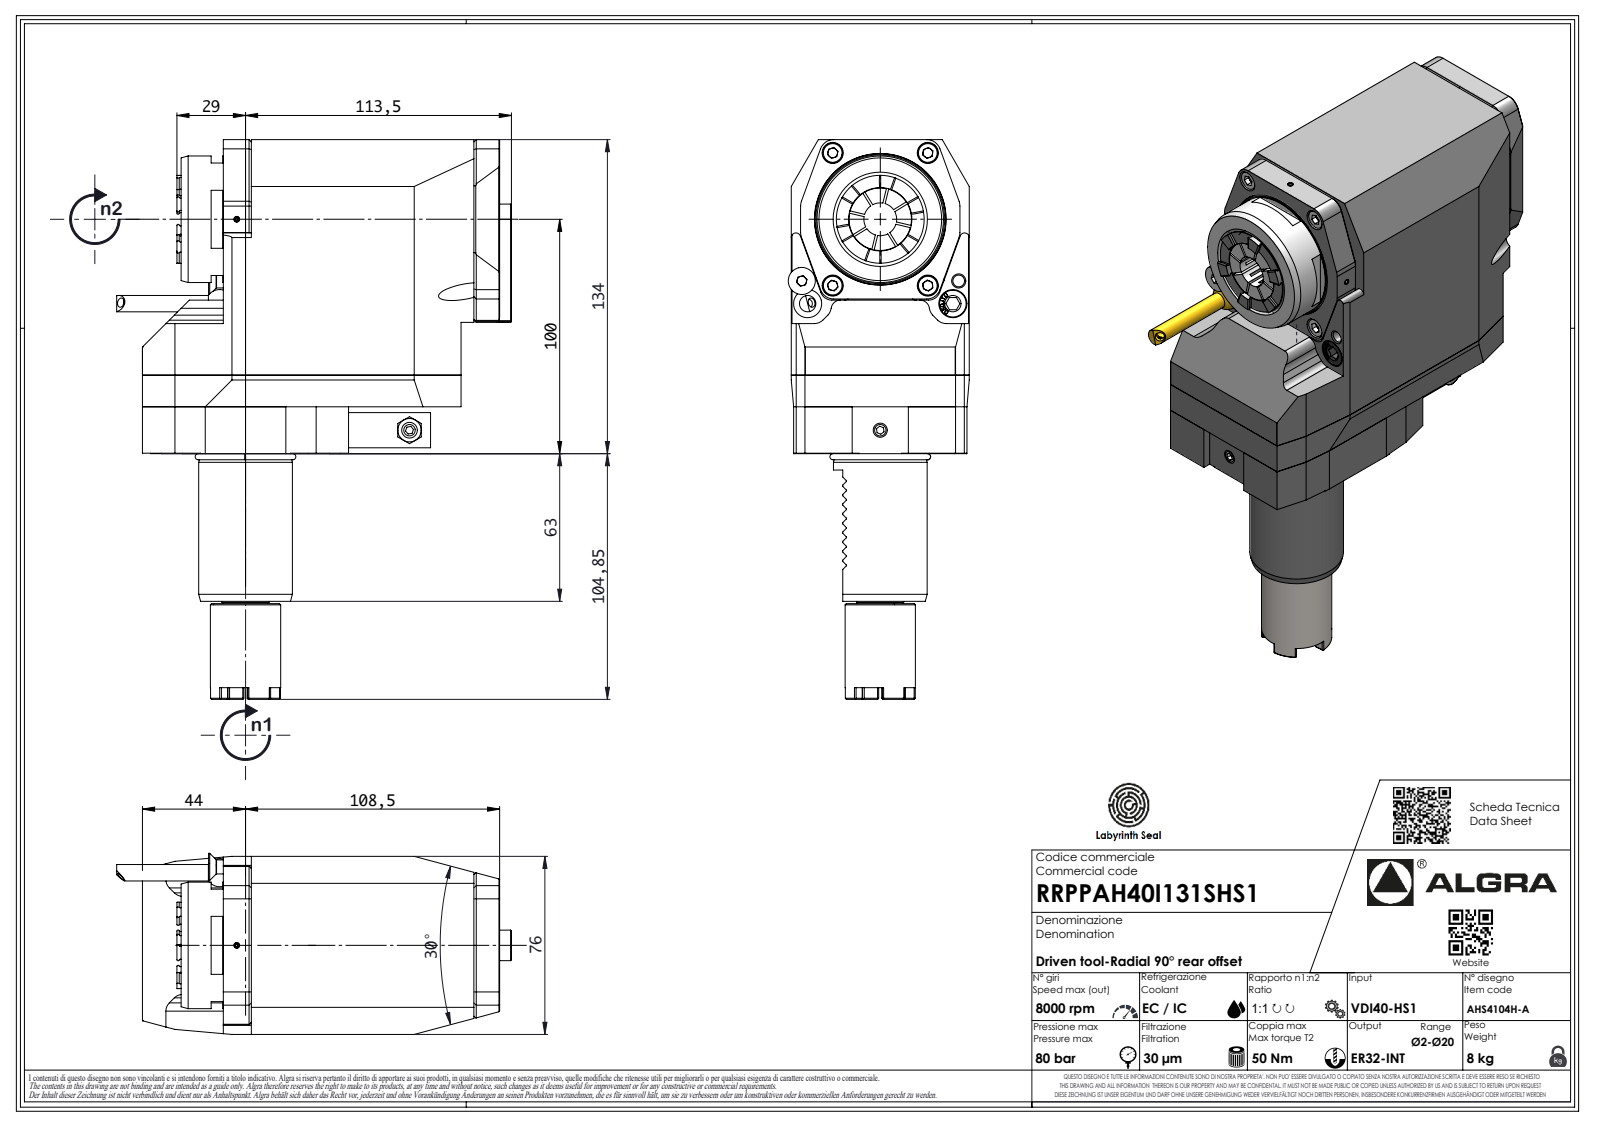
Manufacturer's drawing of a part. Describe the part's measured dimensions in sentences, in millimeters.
The part is named "RRPPAH40I131SHS1". Its 3-D file was written by "SolidWorks 2023 (AUTOMOTIVE_DESIGN)". It is 1 solid with 676 faces: 454 planar, 83 cylindrical and 139 other. Overall it measures 238.85 by 168.5 by 76 millimeters. Its volume is 1 292 000 cubic millimeters and its surface area 92 781 square millimeters. Round holes: 1 of diameter 2.1, 1 of diameter 4, 1 of diameter 5. Round bosses or shafts: 1 of diameter 54, 1 of diameter 40, 1 of diameter 38.7, 1 of diameter 30, 1 of diameter 26.09, 1 of diameter 7, 1 of diameter 6.37, 1 of diameter 6. Partial cylindrical surfaces (rounded edges, fillets, slot ends): 10 of radius 0.3, 10 of radius 6, 7 of radius 0.33, 7 of radius 0.52, 7 of radius 3.7, 6 of radius 5, 3 of radius 2, 2 of radius 0.5. The main face-to-face distances are 76, 16.5, 136, 20, 134, 114, 18, 152.5, 34.5, 17.5.
